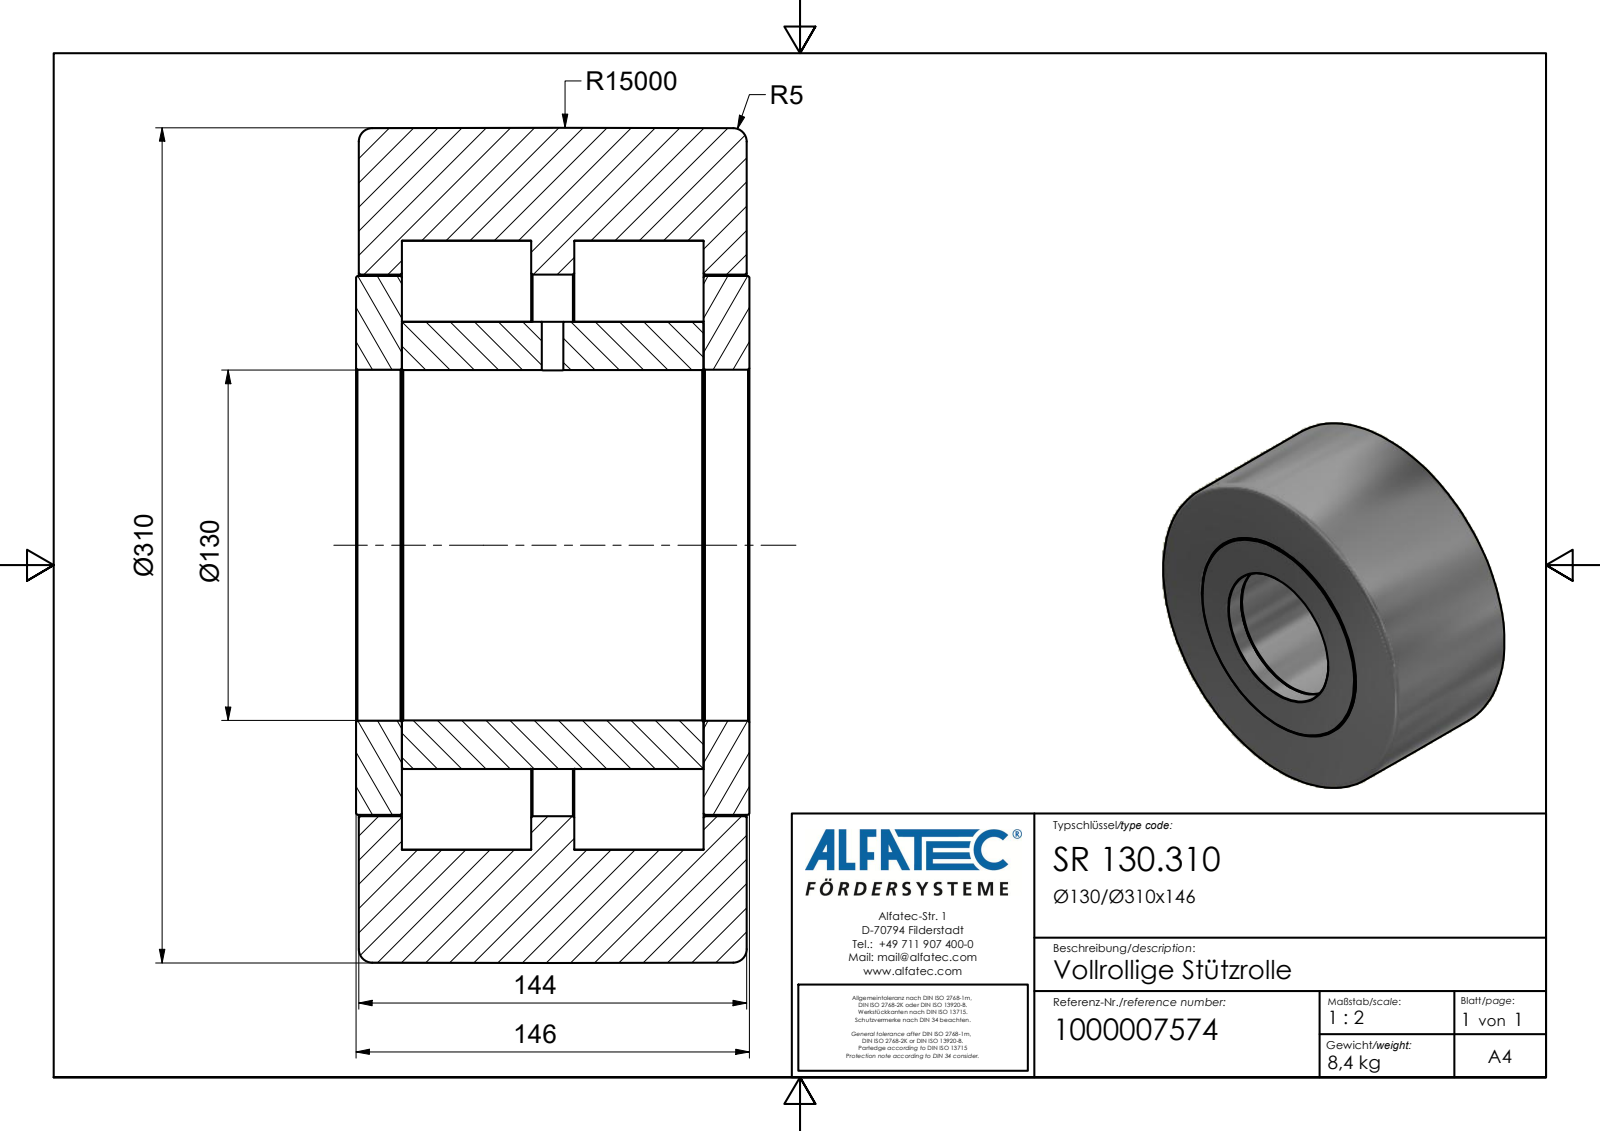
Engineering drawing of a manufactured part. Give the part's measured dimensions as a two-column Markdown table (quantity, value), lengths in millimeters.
| quantity | value |
| --- | --- |
| part name | SR 130.310_Kontur |
| STEP written by | Autodesk Inventor 2020 (AUTOMOTIVE_DESIGN) |
| units | millimeters |
| bodies | 44 solids, 245 faces (92 planar, 52 cylindrical, 101 other) |
| overall size | 310 × 310 × 146 |
| volume | 8 384 000 mm³ |
| surface area | 818 209 mm² |
| round holes (diameter × count) | 8 × 1, 130 × 1, 130.3 × 1, 201 × 1, 226 × 1 |
| round bosses / shafts (diameter × count) | 30 × 20, 200 × 1, 166 × 1 |
| main face-to-face distances | 16, 64, 128, 112, 80, 48, 144, 1, 17, 65 |
